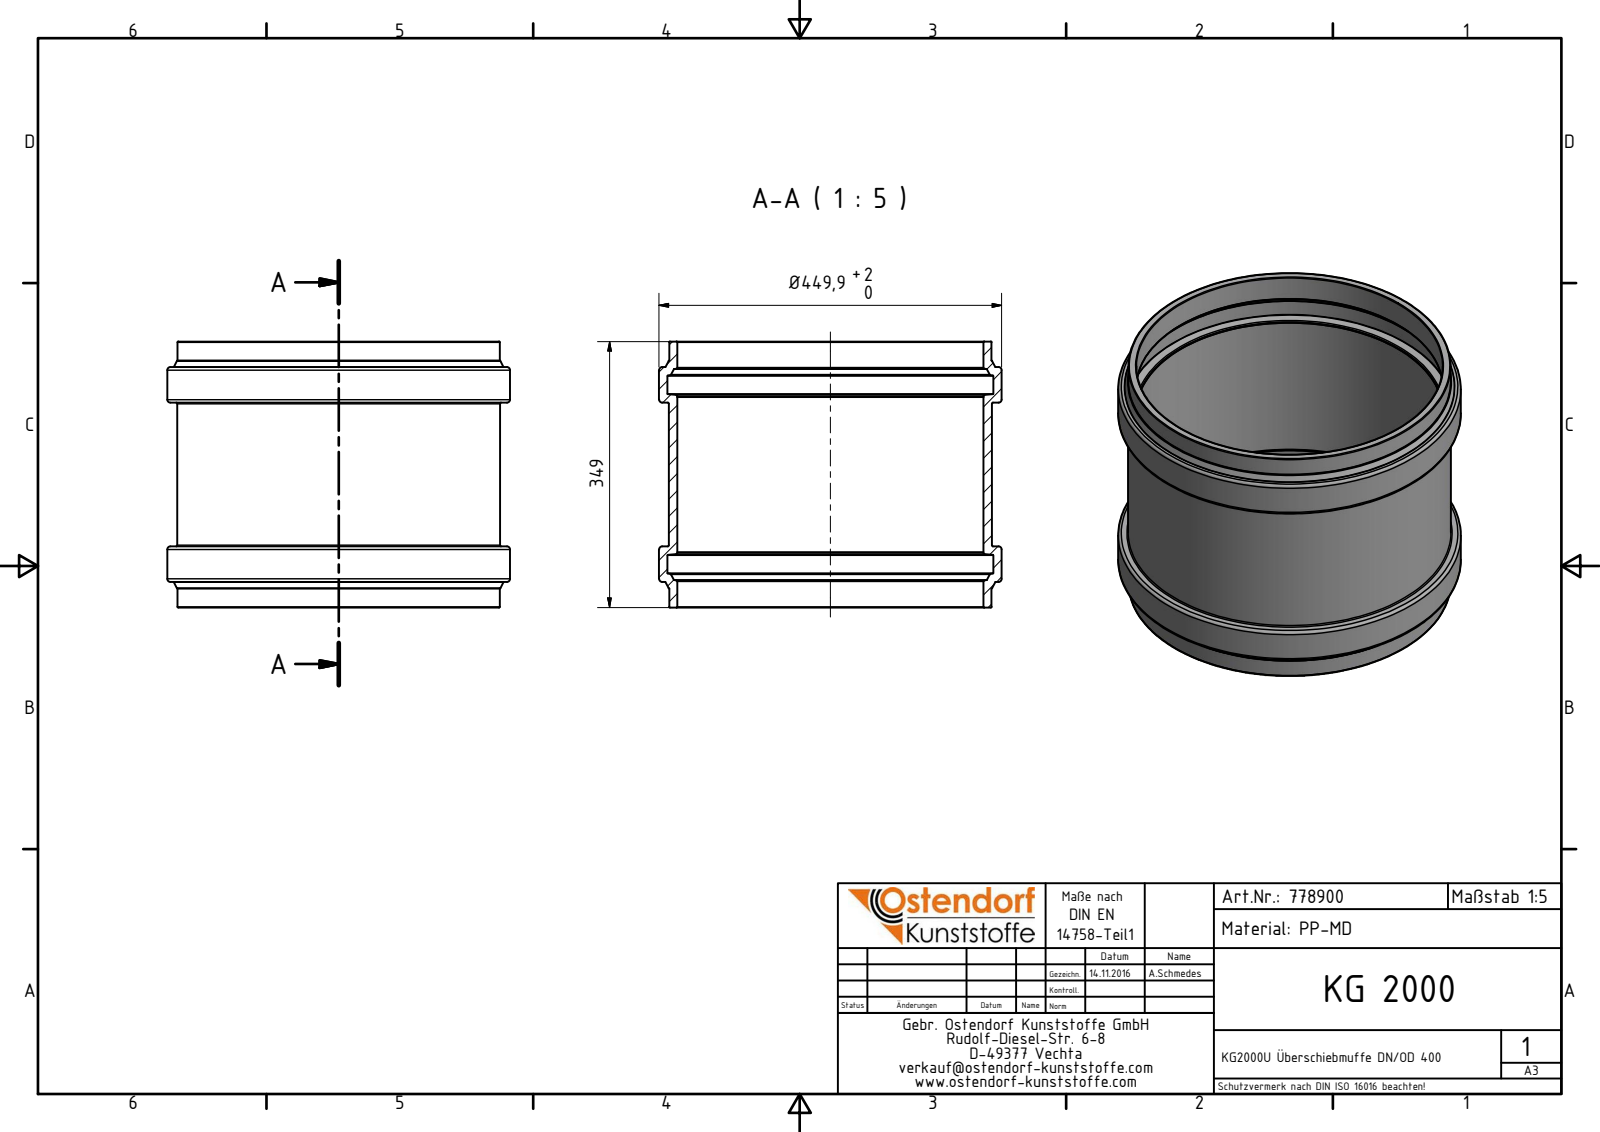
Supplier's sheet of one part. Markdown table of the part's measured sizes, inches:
| quantity | value |
| --- | --- |
| part name | 778900 KG2000U Überschiebmuffe DN_OD 400 |
| STEP written by | Autodesk Inventor 2016 (AUTOMOTIVE_DESIGN) |
| units | inches |
| bodies | 1 solid, 58 faces (8 planar, 12 cylindrical, 38 other) |
| overall size | 17.713 × 17.713 × 13.74 |
| volume | 346.1 in³ |
| surface area | 1 618 in² |
| round holes (diameter × count) | 15.815 × 1, 15.831 × 1, 16.839 × 1 |
| round bosses / shafts (diameter × count) | 17.713 × 1, 16.689 × 1, 16.656 × 1 |
| main face-to-face distances | 3.157, 10.583, 1.323, 12.417, 1.835, 9.26, 13.74, 7.425, 11.094, 2.862 |
